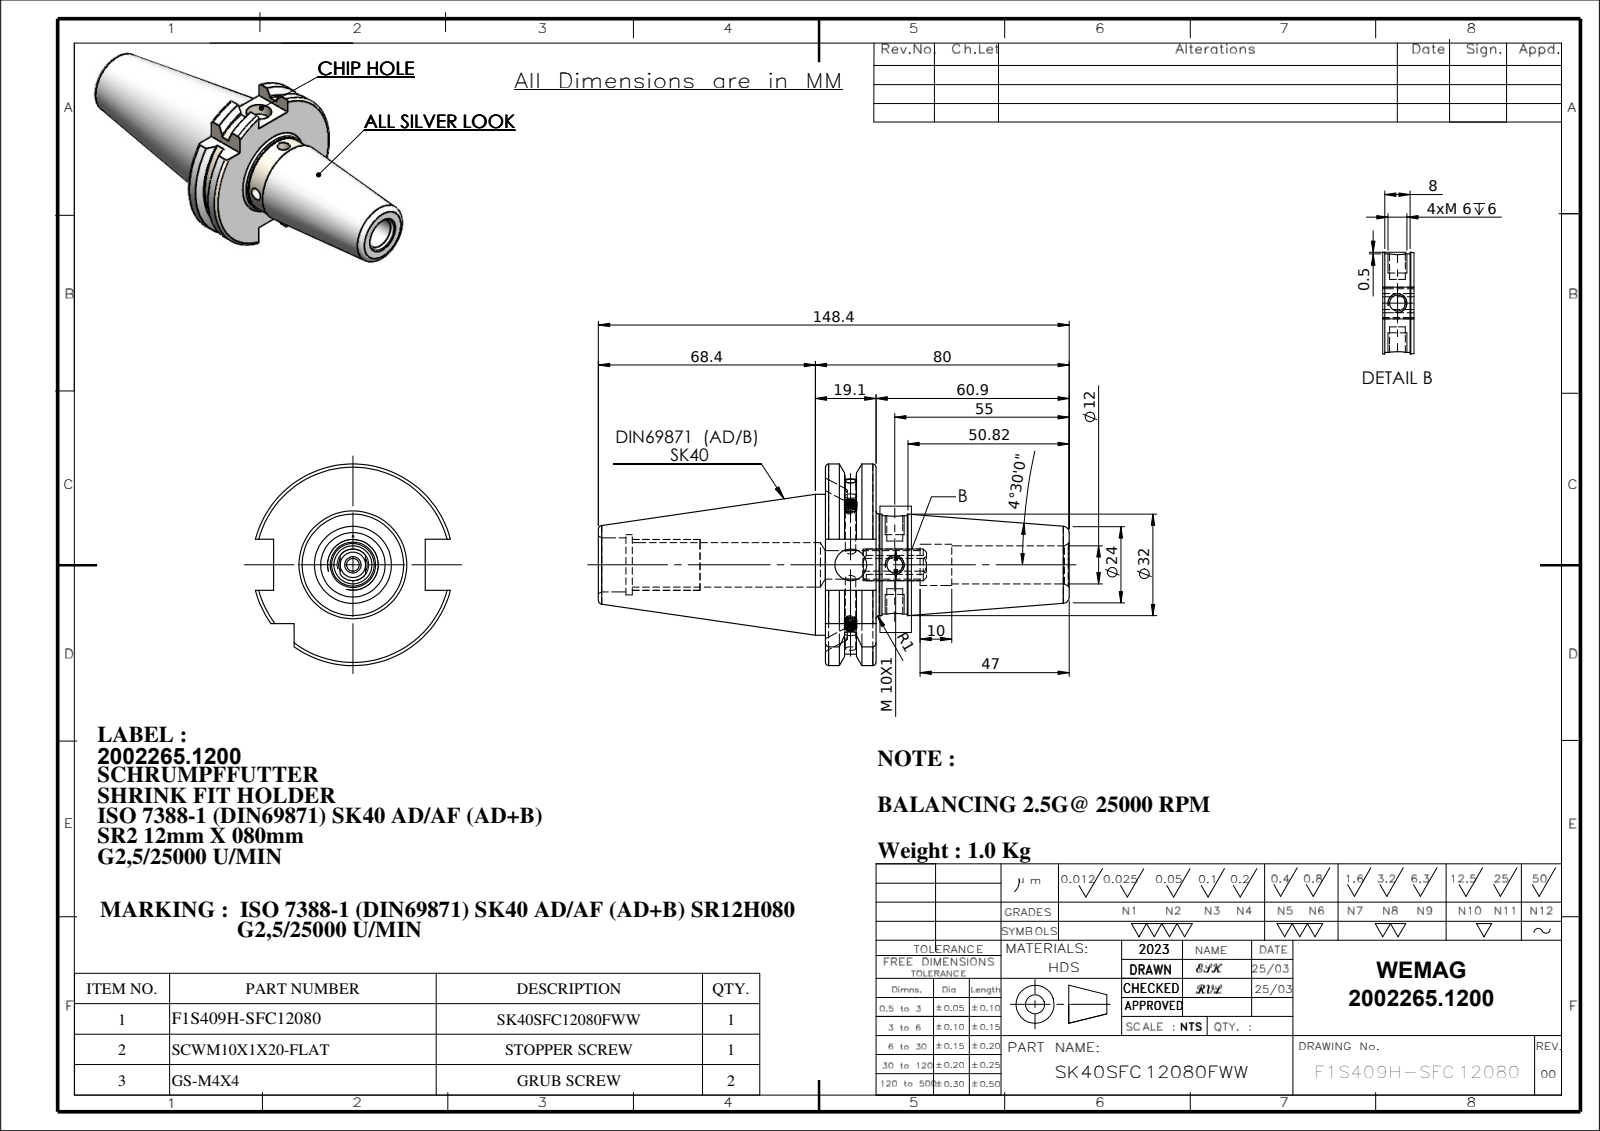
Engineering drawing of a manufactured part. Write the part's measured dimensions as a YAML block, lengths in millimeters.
part_name: "91406-SR212080; SK40SFC12080FWW; GS-M4X4_DIN 913 - M4 x 4-N; SCWM10X1X20-FLAT"
step_written_by: "SolidWorks 2018 (CONFIG_CONTROL_DESIGN)"
units: millimeters
bodies: {solids: 4, faces: 231, planar: 58, cylindrical: 71, other: 102}
overall_size: [148.4, 63.55, 61.48]
volume: 133129
surface_area: 30159
round_holes:
  - {diameter: 5, count: 2}
  - {diameter: 3.3, count: 1}
  - {diameter: 4, count: 1}
  - {diameter: 9, count: 1}
  - {diameter: 10, count: 1}
  - {diameter: 11.99, count: 1}
  - {diameter: 12.99, count: 1}
  - {diameter: 14, count: 1}
  - {diameter: 17, count: 1}
  - {diameter: 19, count: 1}
round_bosses_or_shafts:
  - {diameter: 4, count: 2}
  - {diameter: 44.45, count: 1}
  - {diameter: 32, count: 1}
  - {diameter: 31, count: 1}
partial_cylinders:
  - {radius: 5, count: 1}
  - {radius: 28.12, count: 1}
  - {radius: 31.77, count: 1}
face_to_face_distances: [15.9, 60.9, 76.8, 8, 16.1, 47.8, 71.6, 87.5, 148.4, 10.7]
hole_center_spacings: [13.85]
